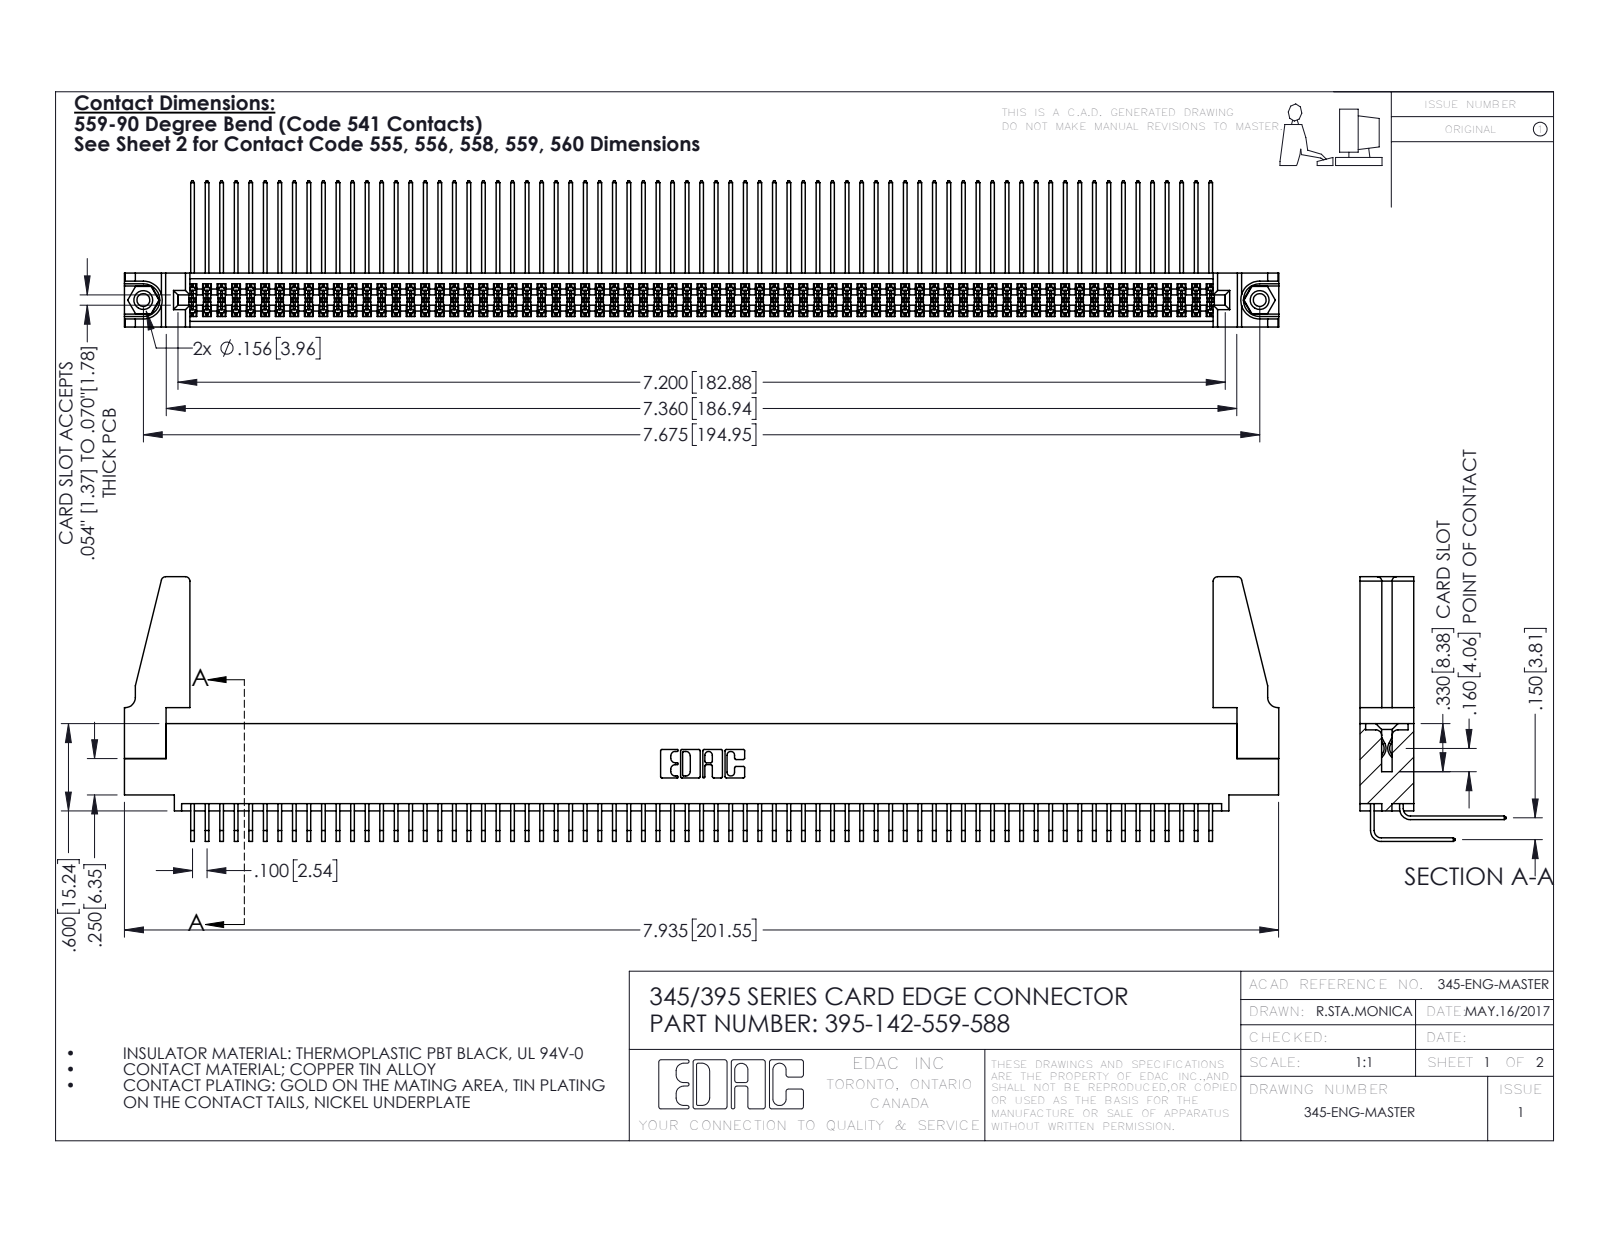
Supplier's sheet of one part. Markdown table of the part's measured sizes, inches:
| quantity | value |
| --- | --- |
| part name | 395-142-559-588; 345-250-001_345-250-001-102; 345-220-078_345-220-088; 345-292-001_559 Tail - 2 (+2 more) |
| STEP written by | SolidWorks 2016 (CONFIG_CONTROL_DESIGN) |
| units | inches |
| bodies | 147 solids, 7638 faces (5126 planar, 2496 cylindrical, 16 other) |
| overall size | 7.936 × 1.819 × 1.005 |
| volume | 1.455 in³ |
| surface area | 59.01 in² |
| round holes (diameter × count) | 0.089 × 2, 0.125 × 2, 0.156 × 2, 0.064 × 1 |
| round bosses / shafts (diameter × count) | 0.155 × 2 |
| partial cylindrical surfaces (radius × count) | 0.006 × 284, 0.01 × 22, 0.03 × 8, 0.007 × 6, 0.031 × 6, 0.026 × 3, 0.014 × 2, 0.019 × 2 |
| main face-to-face distances | 0.072, 0.298, 0.37, 0.098, 0.272, 0.025, 0.2, 0.225, 0.175, 0.15 |
| hole center spacings | 0.27, 7.439, 7.675 |
